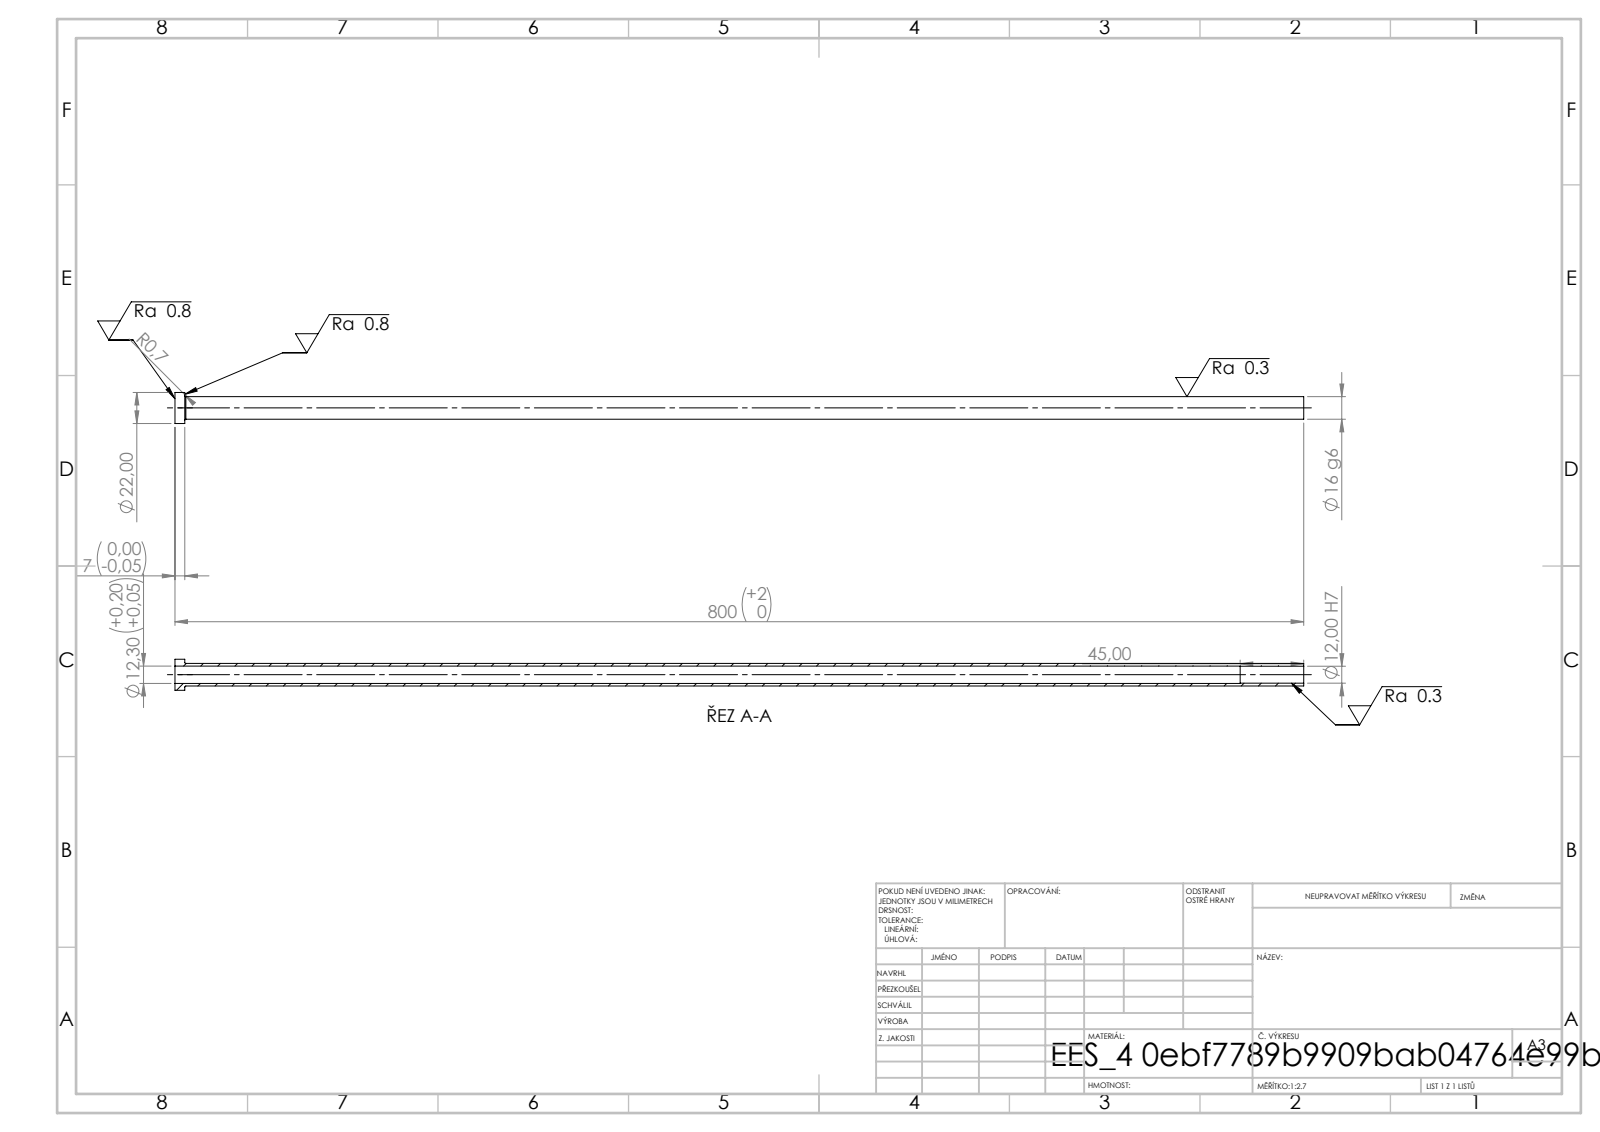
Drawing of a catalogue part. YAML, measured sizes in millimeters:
step_written_by: "SolidWorks 2019 (CONFIG_CONTROL_DESIGN)"
units: millimeters
bodies: {solids: 1, faces: 14, planar: 4, cylindrical: 8, other: 2}
overall_size: [800, 22, 22]
volume: 67308
surface_area: 71734
round_holes:
  - {diameter: 12, count: 1}
  - {diameter: 12.3, count: 1}
round_bosses_or_shafts:
  - {diameter: 22, count: 1}
  - {diameter: 16, count: 1}
face_to_face_distances: [7, 800, 793, 755, 748, 45]
